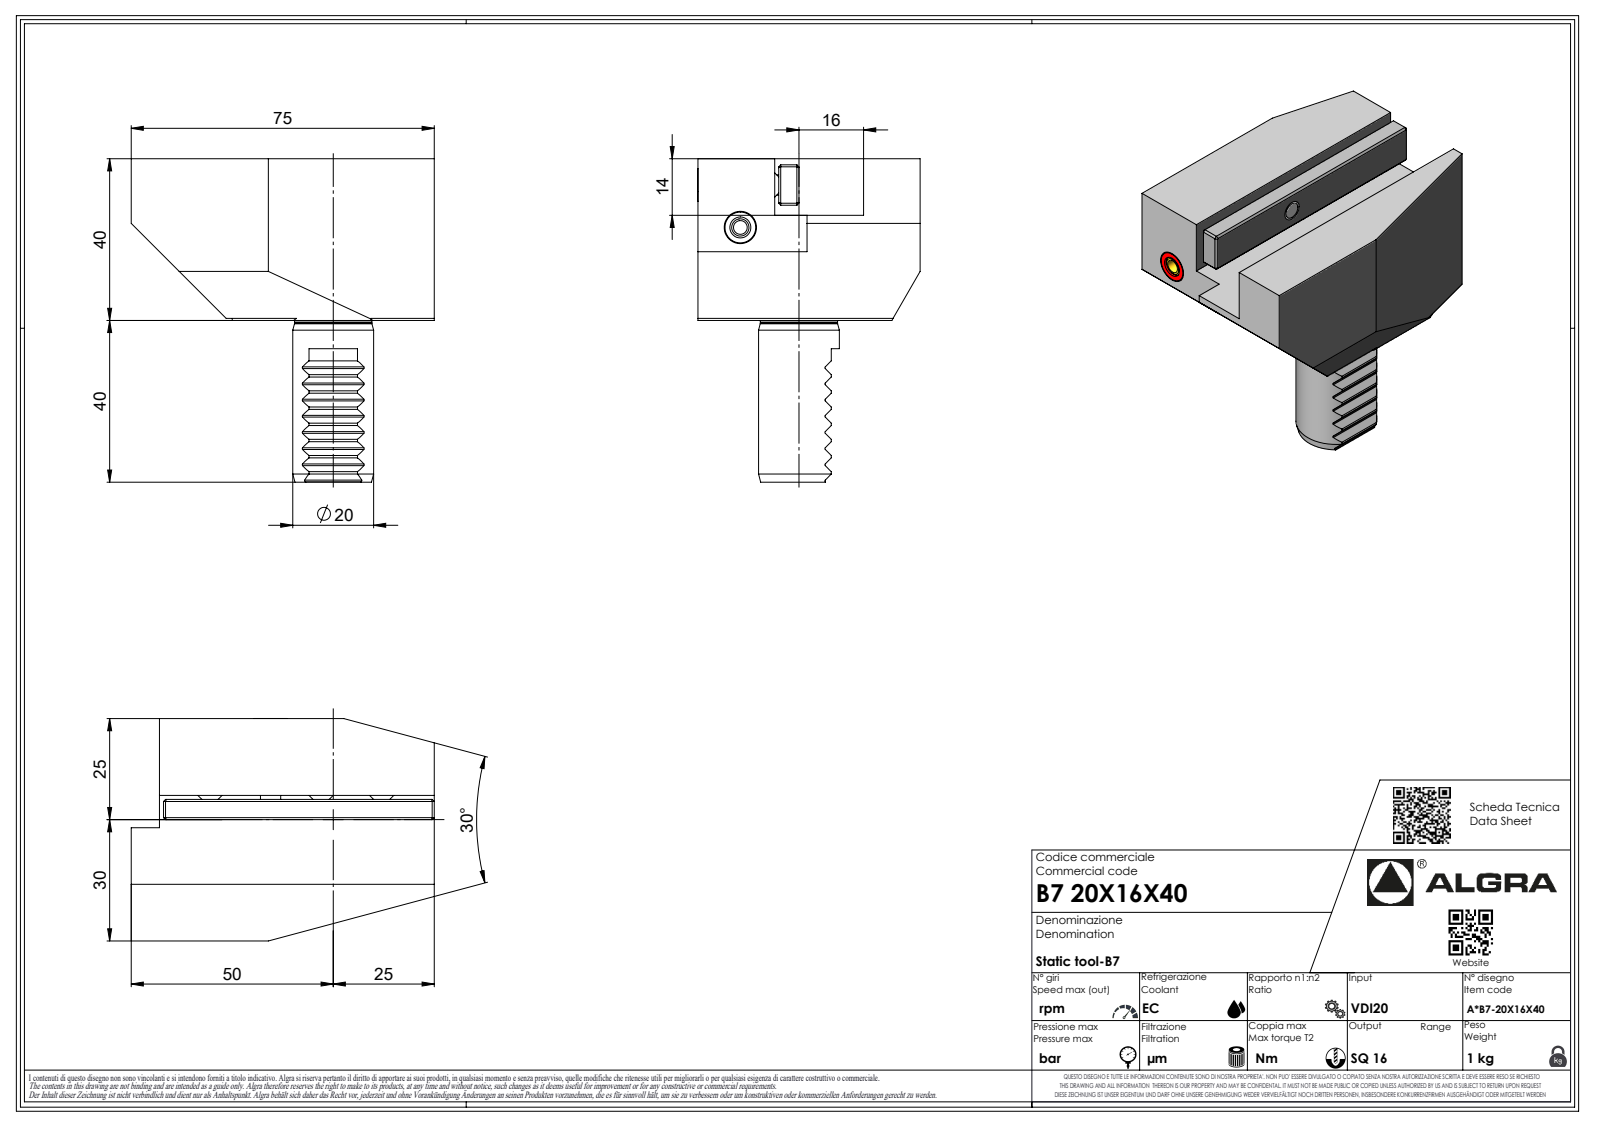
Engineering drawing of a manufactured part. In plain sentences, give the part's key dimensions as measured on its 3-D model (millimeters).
The part is named "B720X16X40". Its 3-D file was written by "SolidWorks 2023 (AUTOMOTIVE_DESIGN)". It is 1 solid with 340 faces: 250 planar, 38 cylindrical and 52 other. Overall it measures 80 by 75 by 55 millimeters. Its volume is 125 769 cubic millimeters and its surface area 20 646 square millimeters. Round holes: 1 of diameter 2.1. Round bosses or shafts: 1 of diameter 50, 1 of diameter 20, 1 of diameter 19.1, 1 of diameter 6.37, 1 of diameter 1.7. Partial cylindrical surfaces (rounded edges, fillets, slot ends): 8 of radius 0.3, 7 of radius 0.33, 7 of radius 0.52, 7 of radius 3.7, 1 of radius 0.21. The main face-to-face distances are 14, 40, 26, 41, 55, 0.5, 25, 16, 30, 68.
